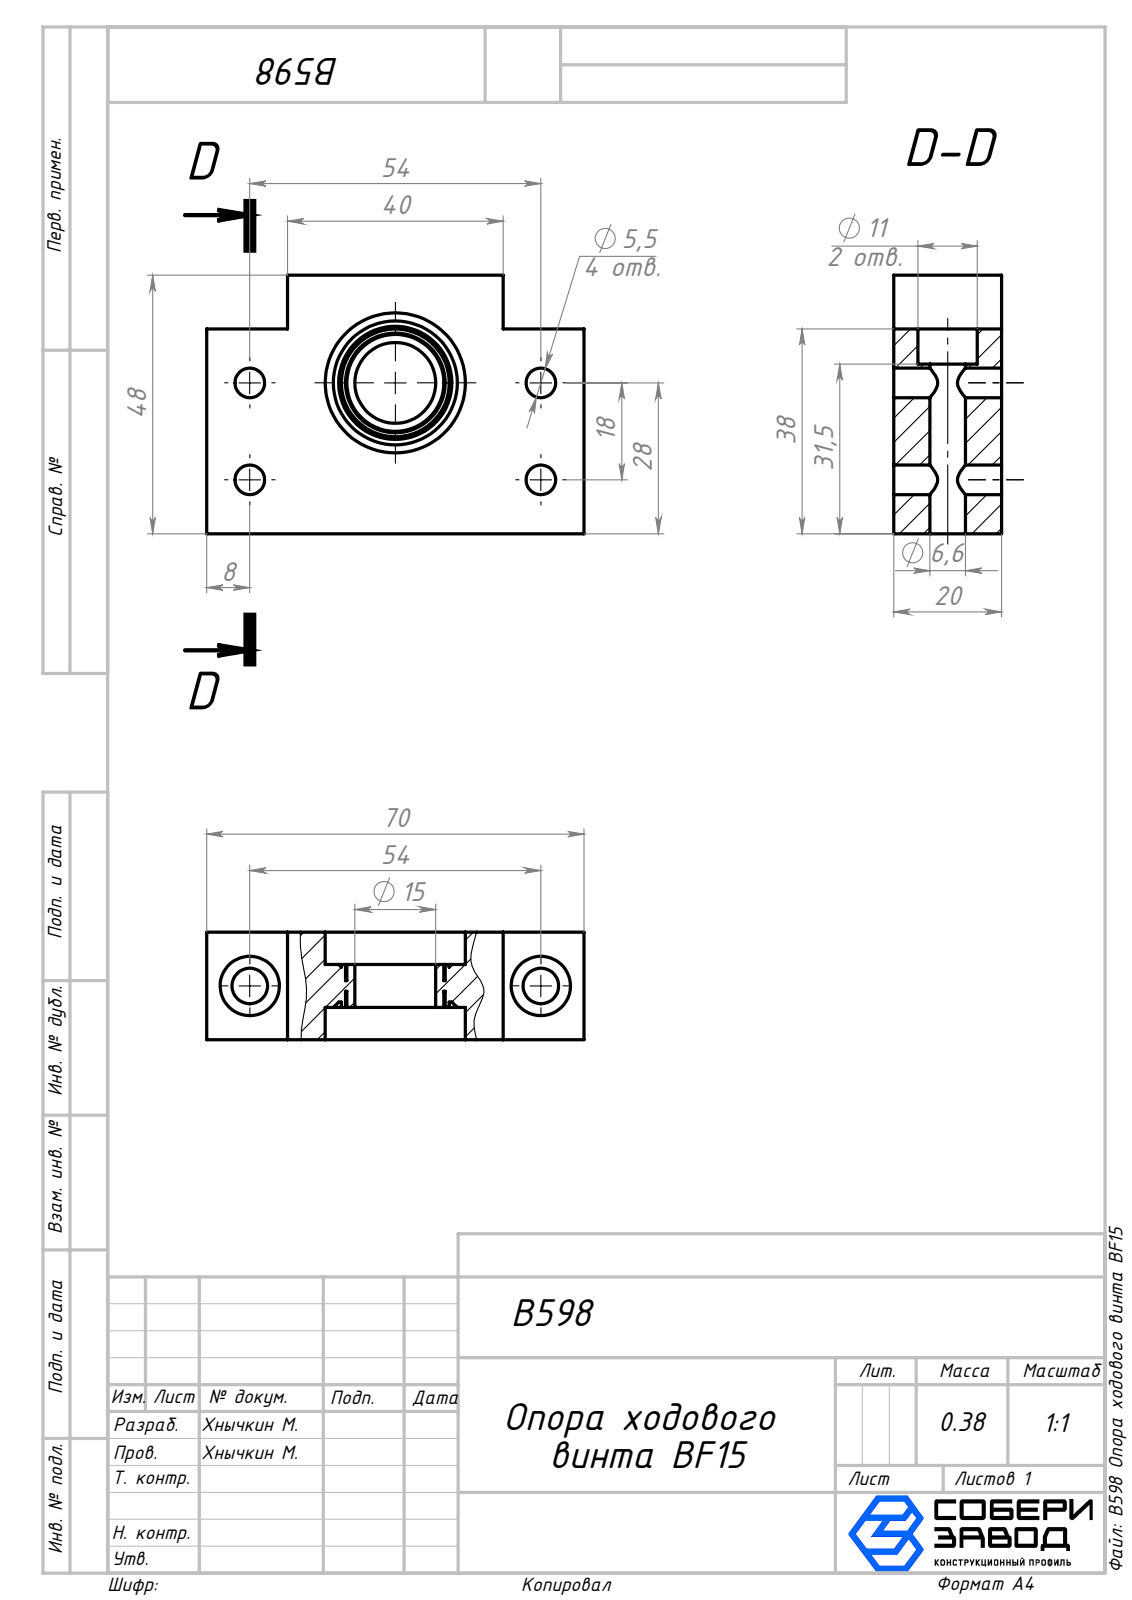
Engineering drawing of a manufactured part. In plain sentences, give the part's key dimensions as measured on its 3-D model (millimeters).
The part is named "B598 Опора ходового винта BF15". Its 3-D file was written by "SolidWorks 2026 (AUTOMOTIVE_DESIGN)". It is 1 solid with 67 faces: 21 planar, 42 cylindrical and 4 other. Overall it measures 70 by 48 by 20 millimeters. Its volume is 48 530 cubic millimeters and its surface area 14 904 square millimeters. Round holes: 4 of diameter 5.5, 2 of diameter 6.6, 2 of diameter 11, 1 of diameter 15, 1 of diameter 18.5, 1 of diameter 26. Round bosses or shafts: 1 of diameter 20, 1 of diameter 18. The main face-to-face distances are 20, 48, 70, 6, 14, 38, 10, 15, 55, 8. The hole center spacings are 54, 18, 27, 32.45, 56.92.
